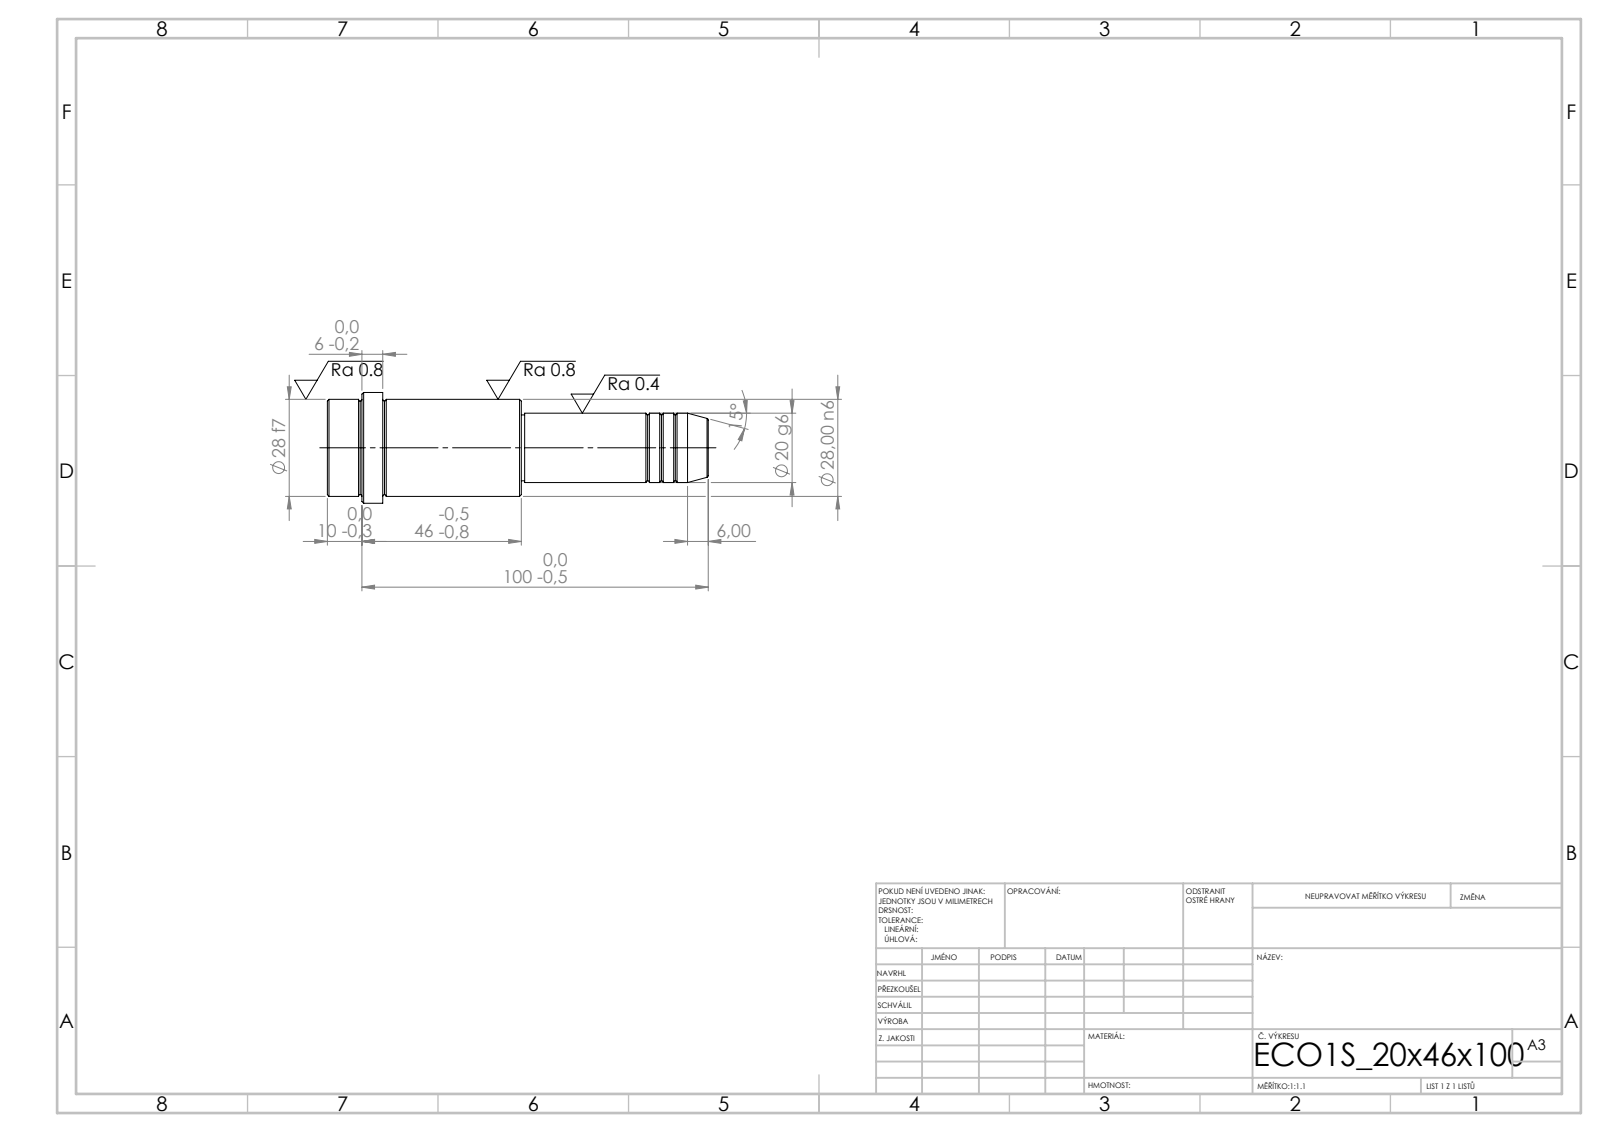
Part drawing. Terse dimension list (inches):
written by: SolidWorks 2019 (CONFIG_CONTROL_DESIGN)
unit: in
bodies: 1 solid, 52 faces (6 planar, 16 cylindrical, 30 other)
size: 4.331 × 1.26 × 1.26
volume: 3.178 in³; area: 15.58 in²
bosses: 1× ⌀1.26, 1× ⌀1.102, 1× ⌀0.787, 1× ⌀0.748
face distances: 2.205, 2.126, 4.331, 3.701, 1.575, 0.63, 3.937, 1.811, 0.236, 0.394
